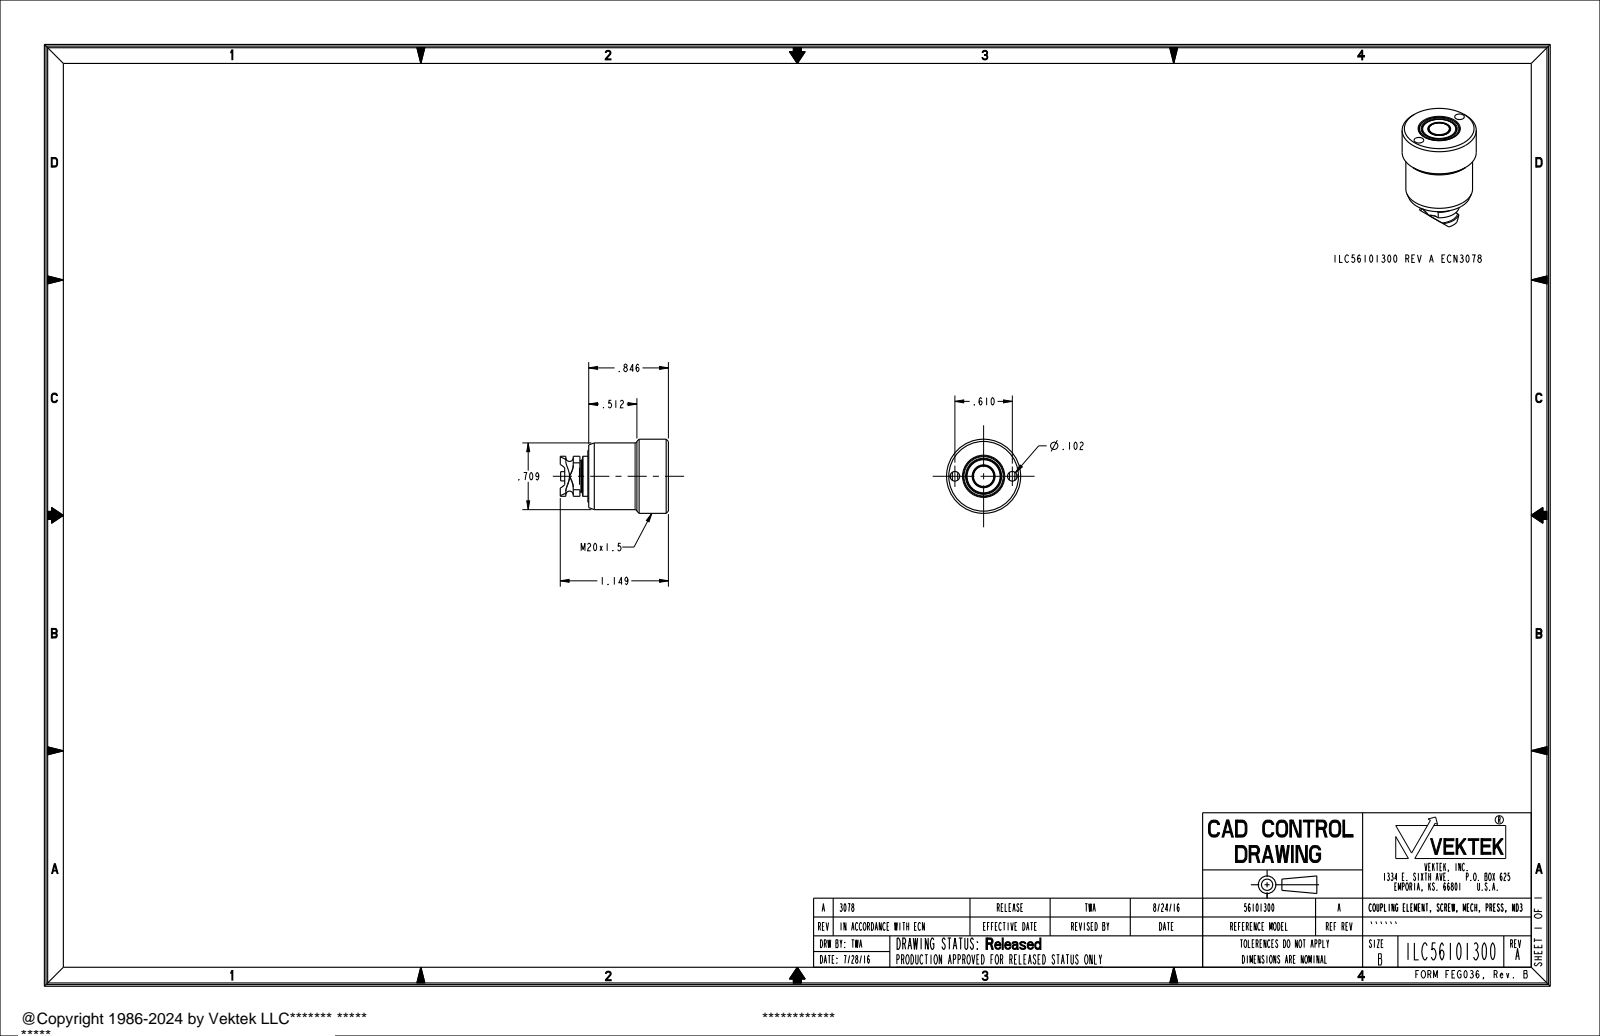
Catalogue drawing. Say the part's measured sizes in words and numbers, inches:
The part is named "ILC56101300". Its 3-D file was written by "PRO/ENGINEER BY PARAMETRIC TECHNOLOGY CORPORATION, 2013320 (CONFIG_CONTROL_DESIGN)". It is 0 solids with 96 faces: 23 planar, 34 cylindrical and 39 other. Overall it measures 1.149 by 0.787 by 0.787 inches. Round holes: 2 of diameter 0.102, 1 of diameter 0.398, 1 of diameter 0.425, 1 of diameter 0.551. Round bosses or shafts: 1 of diameter 0.787, 1 of diameter 0.709, 1 of diameter 0.368, 1 of diameter 0.359, 1 of diameter 0.335, 1 of diameter 0.23, 1 of diameter 0.217, 1 of diameter 0.098. Partial cylindrical surfaces (rounded edges, fillets, slot ends): 1 of radius 0.138. The main face-to-face distances are 0.846, 0.94, 0.094, 0.856, 0.085, 0.939, 0.924, 0.078, 0.069, 0.016. The hole center spacings are 0.305, 0.61.
